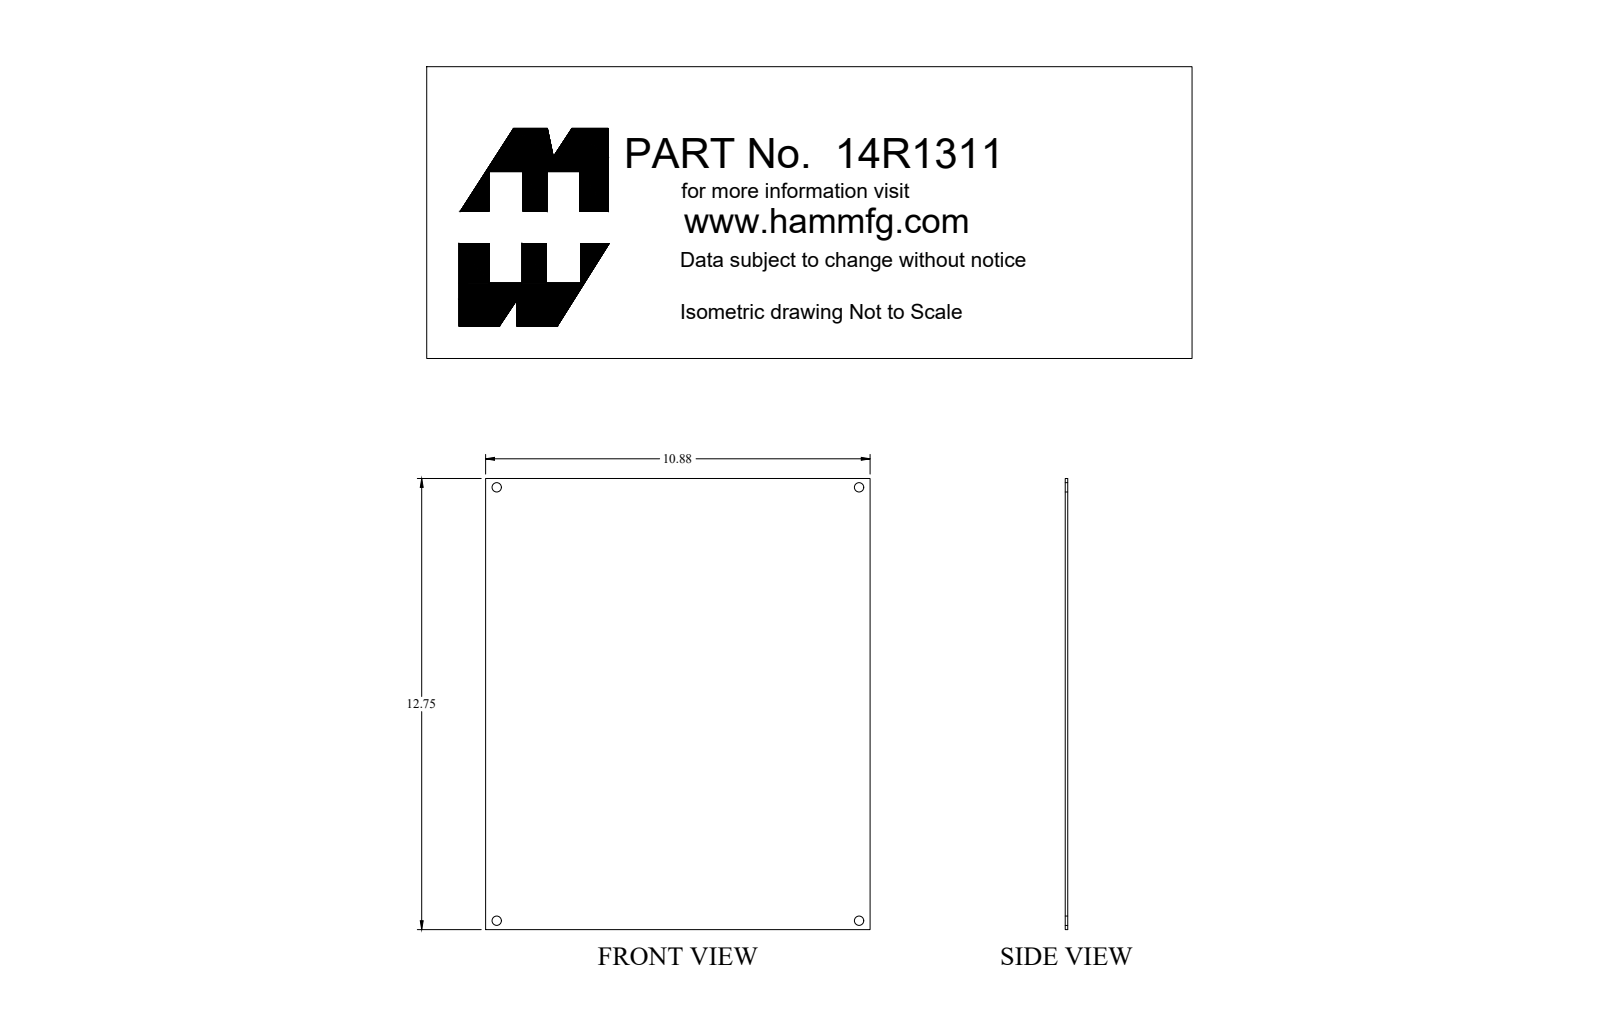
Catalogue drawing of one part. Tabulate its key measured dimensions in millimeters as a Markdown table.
| quantity | value |
| --- | --- |
| part name | 14R1311 |
| STEP written by | SolidWorks 2018 (AUTOMOTIVE_DESIGN) |
| units | millimeters |
| bodies | 1 solid, 10 faces (6 planar, 4 cylindrical, 0 other) |
| overall size | 323.9 × 276.2 × 1.8 |
| volume | 163 300 mm³ |
| surface area | 181 000 mm² |
| round holes (diameter × count) | 6.7 × 4 |
| main face-to-face distances | 1.8, 276.2, 323.9 |
| hole center spacings | 260.4, 311.2, 405.7 |
